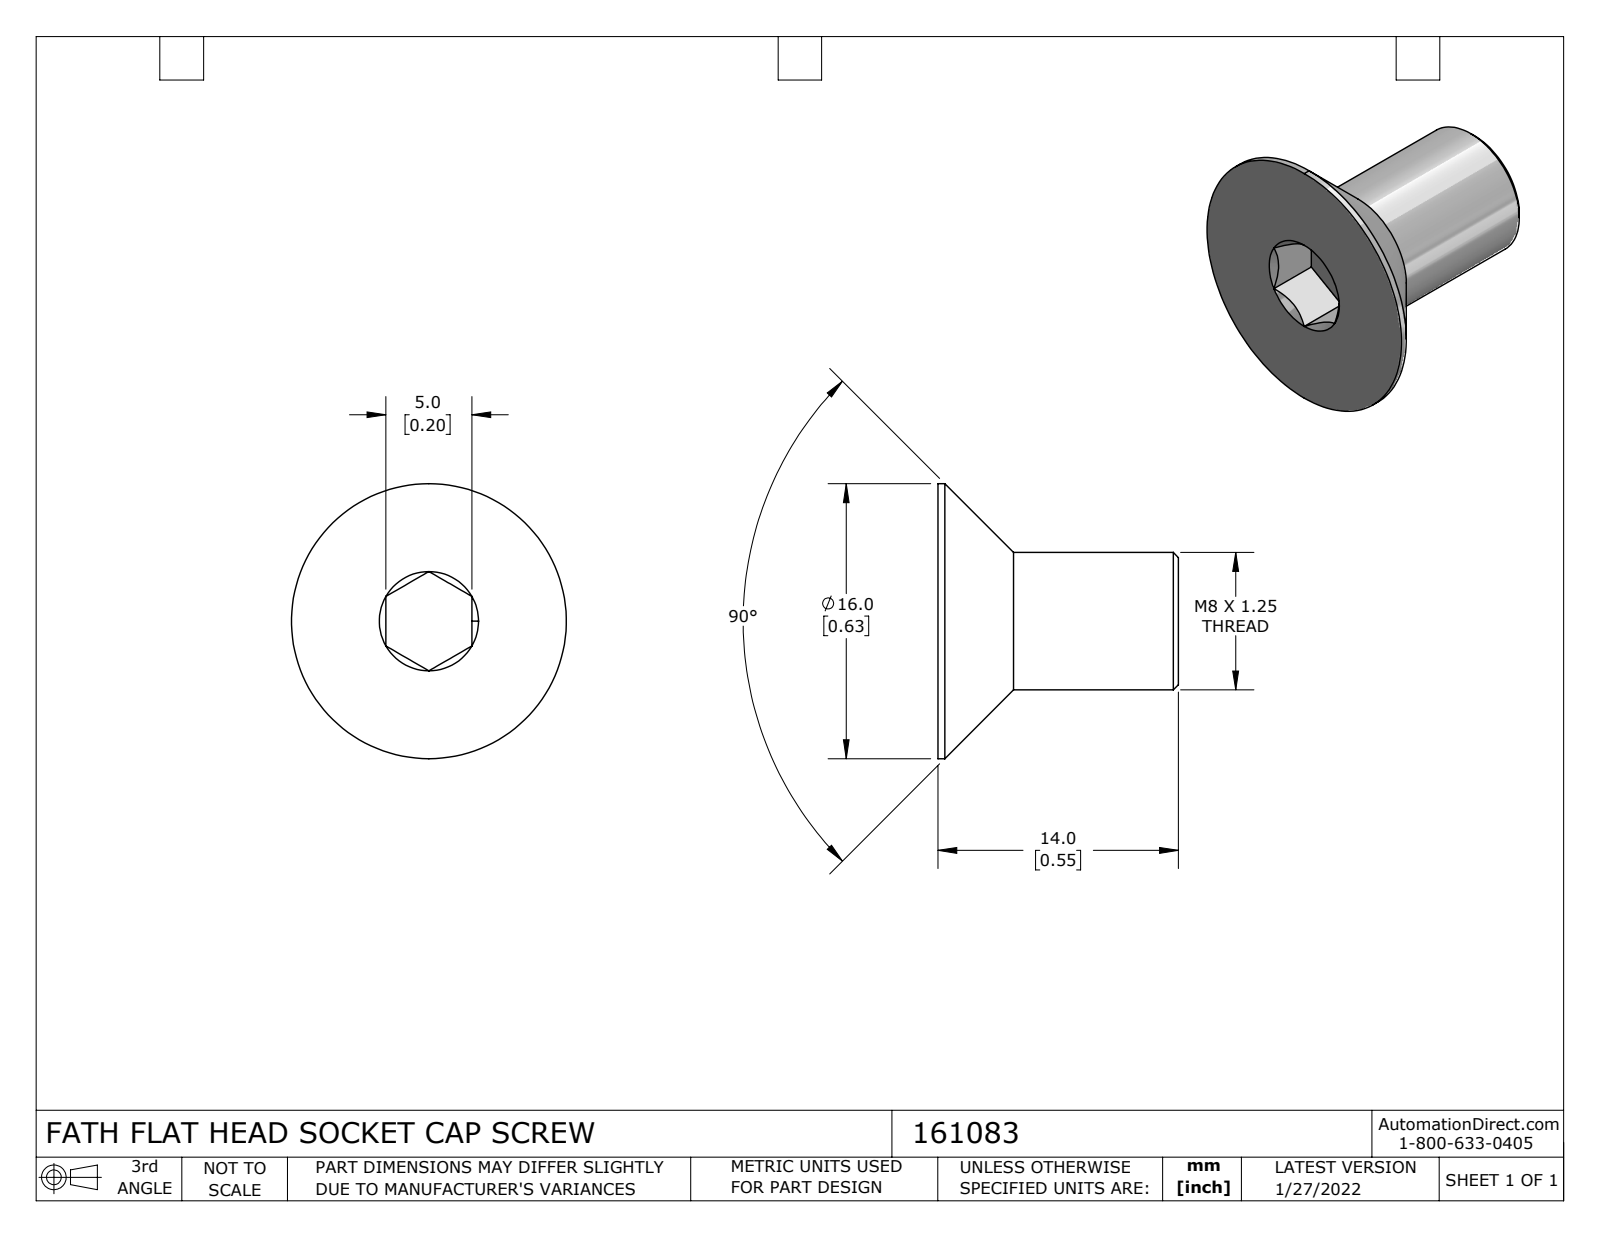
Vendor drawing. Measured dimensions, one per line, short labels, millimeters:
name: 161083
written by: SolidWorks 2021 (CONFIG_CONTROL_DESIGN)
unit: mm
bodies: 1 solid, 24 faces (9 planar, 4 cylindrical, 11 other)
size: 16 × 16 × 14
volume: 964 mm³; area: 772 mm²
bosses: 1× ⌀16, 1× ⌀8
face distances: 14, 5, 10.92, 3.08
